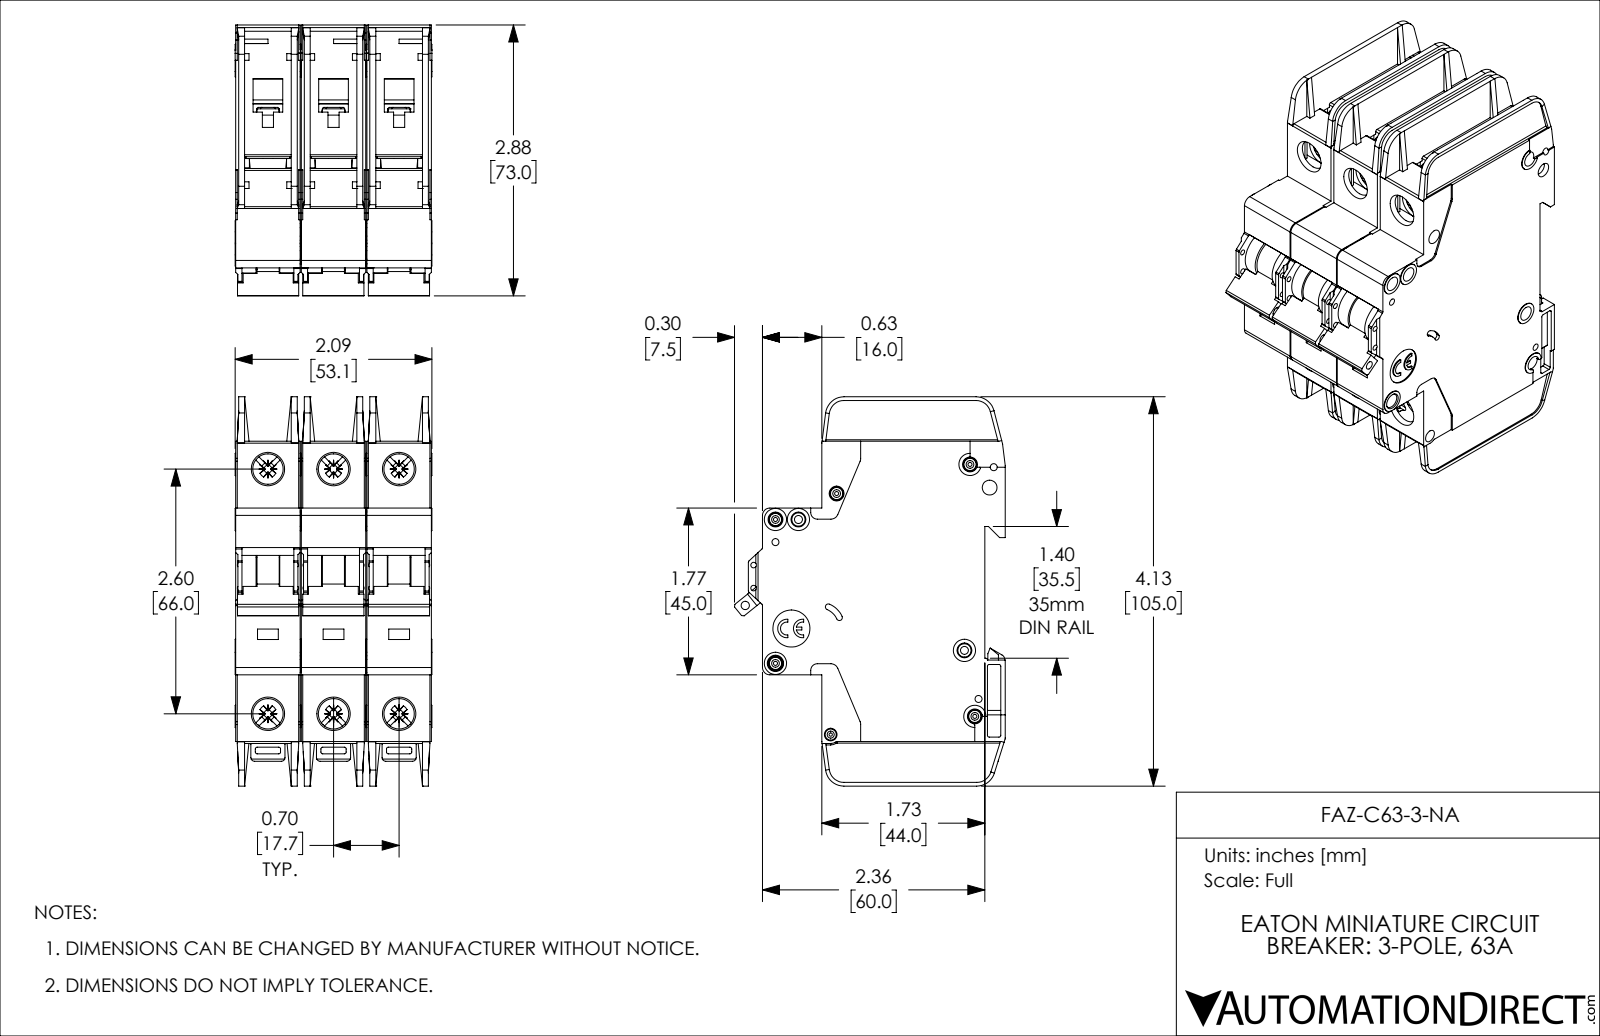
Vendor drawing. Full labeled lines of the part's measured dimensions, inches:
Part name (STEP PRODUCT): FAZ-C63-3-NA
STEP written by: SolidWorks 2019 (AUTOMOTIVE_DESIGN)
Units: inches
Bodies: 3 solids, 3381 faces (2013 planar, 1071 cylindrical, 297 other)
Overall size (bounding box): 4.134 × 2.876 × 2.091
Volume: 14.05 in³ · Surface area: 123 in²
Round holes (diameter × count): ⌀0.157 ×8, ⌀0.323 ×6, ⌀0.043 ×5, ⌀0.075 ×4, ⌀0.059 ×2, ⌀0.085 ×2, ⌀0.035 ×1, ⌀0.089 ×1, ⌀0.098 ×1, ⌀0.134 ×1, ⌀0.394 ×1
Round bosses / shafts (diameter × count): ⌀0.13 ×5, ⌀0.236 ×4, ⌀0.118 ×4, ⌀0.098 ×3
Partial cylindrical surfaces — rounded edges, fillets, slot ends (radius × count): R0.02 ×72, R0.016 ×30, R0.039 ×18, R0.043 ×12, R0.079 ×12, R0.008 ×6, R0.01 ×6, R0.028 ×6
Main face-to-face distances: 0.697, 0.047, 1.394, 0.685, 0.591, 1.382, 0.744, 0.65, 0.106, 0.094
Hole centre spacings: 0.697, 2.69, 2.598, 0.244, 0.537, 0.87, 1.394, 2.948
